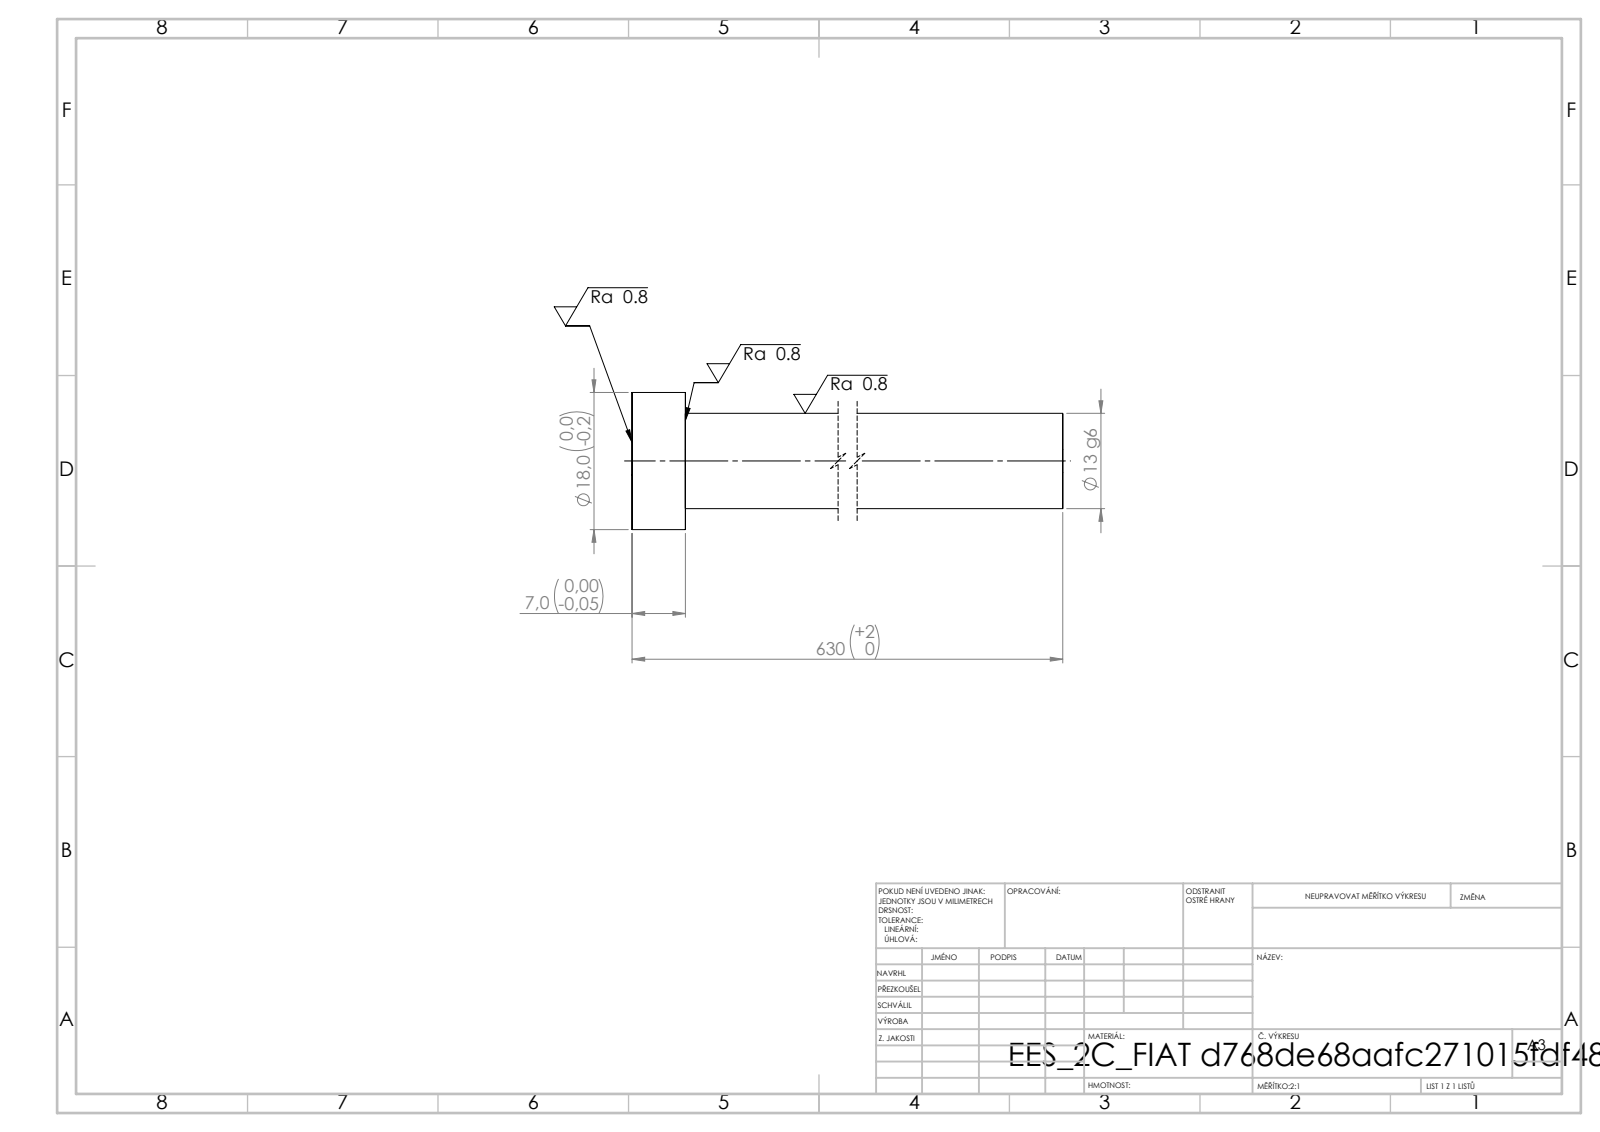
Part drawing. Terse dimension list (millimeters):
written by: SolidWorks 2019 (CONFIG_CONTROL_DESIGN)
unit: mm
bodies: 1 solid, 7 faces (3 planar, 4 cylindrical, 0 other)
size: 630 × 18 × 18
volume: 78 235 mm³; area: 25 370 mm²
bosses: 1× ⌀18, 1× ⌀12.5
face distances: 7, 630, 623
